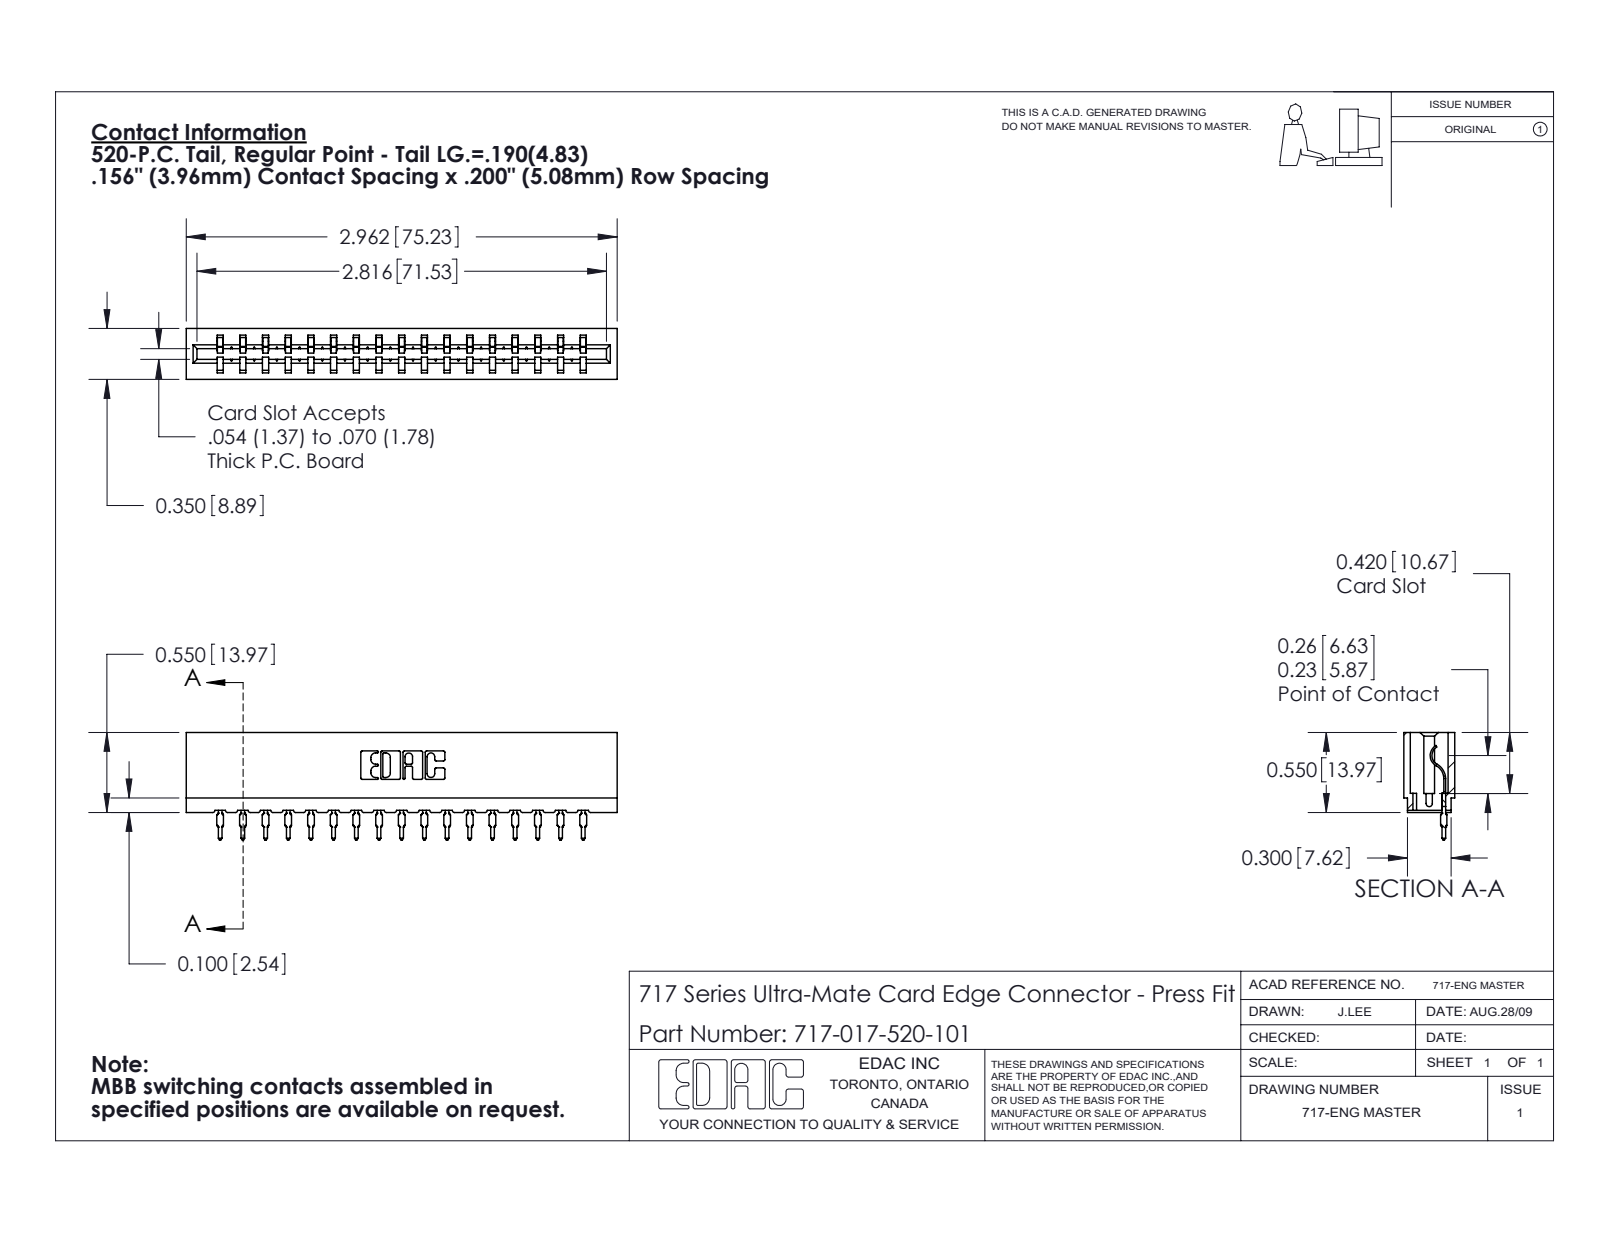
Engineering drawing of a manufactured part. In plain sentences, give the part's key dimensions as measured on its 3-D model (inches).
The part is named "745-292-001_520; 717 Part_Insulator Option - 06; 717-017-520-101". Its 3-D file was written by "SolidWorks 2020 (CONFIG_CONTROL_DESIGN)". It is 18 solids with 2015 faces: 1210 planar, 363 cylindrical and 442 other. Overall it measures 2.962 by 0.739 by 0.35 inches. Its volume is 0.393 cubic inches and its surface area 13.42 square inches. Partial cylindrical surfaces (rounded edges, fillets, slot ends): 34 of radius 0.015, 34 of radius 0.021, 22 of radius 0.01, 6 of radius 0.007, 6 of radius 0.031, 4 of radius 0.005, 4 of radius 0.011, 3 of radius 0.026. The main face-to-face distances are 0.212, 0.138, 0.35, 0.156, 0.624, 0.468, 0.074, 0.198, 0.312, 0.312.
